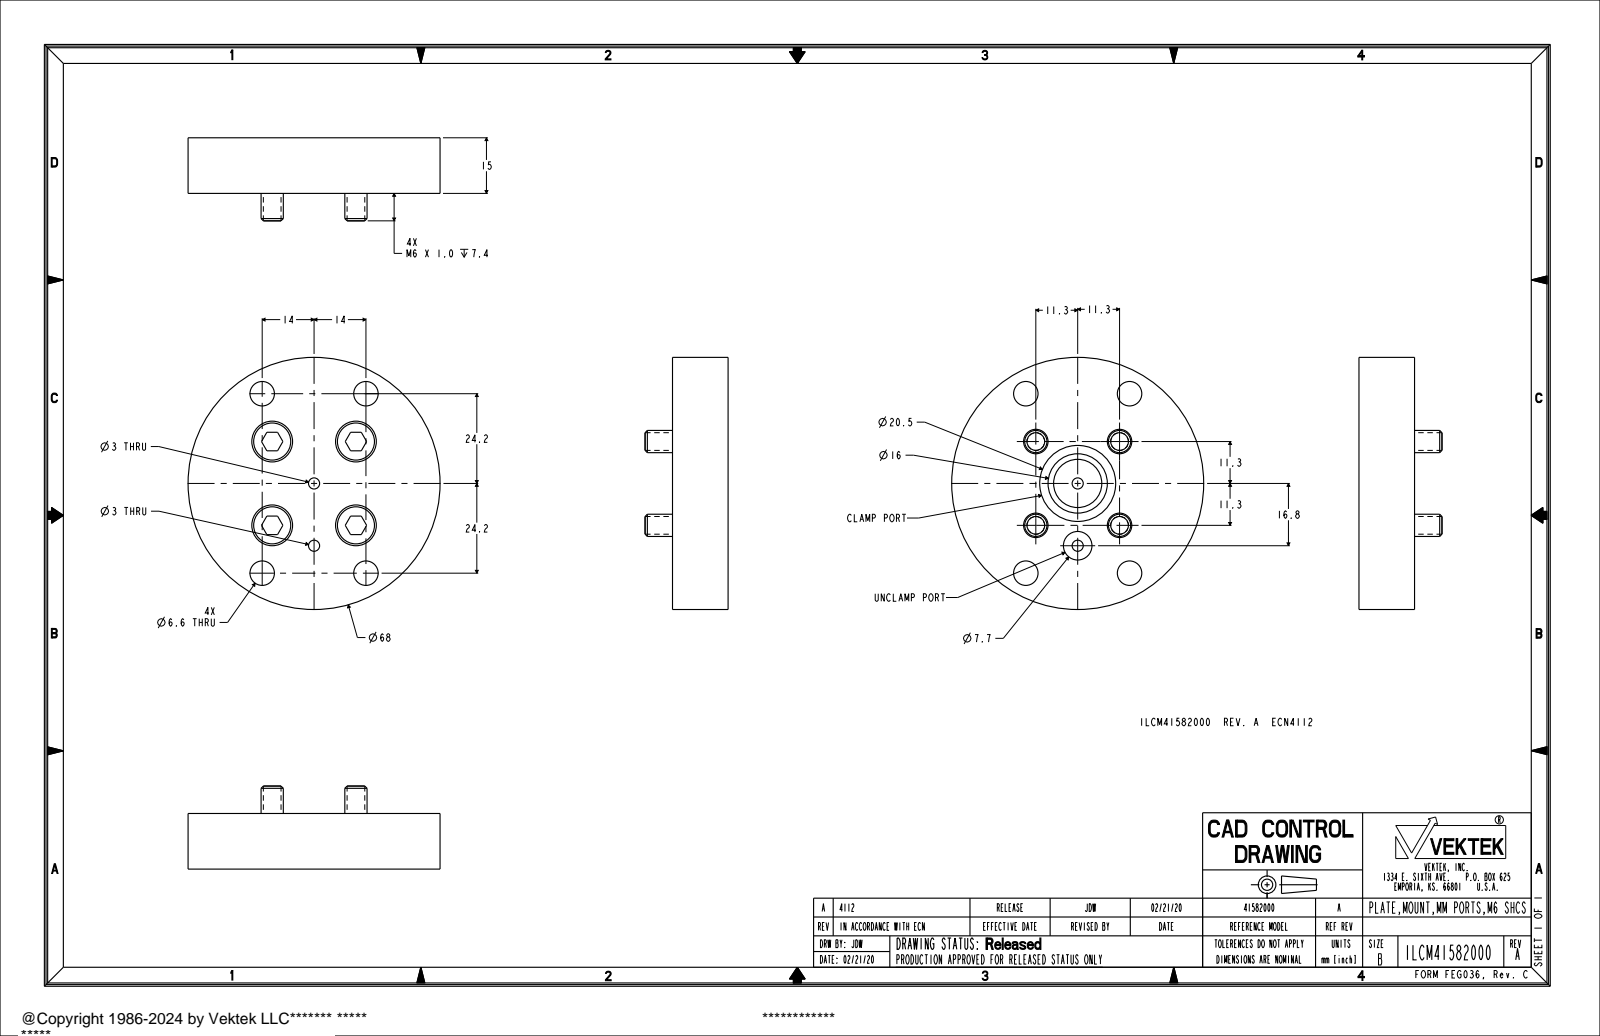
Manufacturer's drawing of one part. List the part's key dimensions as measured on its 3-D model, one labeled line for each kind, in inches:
Part name (STEP PRODUCT): ILCM41582000
STEP written by: PRO/ENGINEER BY PARAMETRIC TECHNOLOGY CORPORATION, 2013320 (AUTOMOTIVE_DESIGN)
Units: inches
Bodies: 1 solid, 127 faces (57 planar, 60 cylindrical, 10 other)
Overall size (bounding box): 2.677 × 2.677 × 0.882
Volume: 3.08 in³ · Surface area: 26 in²
Round holes (diameter × count): ⌀0.26 ×8, ⌀0.433 ×4, ⌀0.118 ×2, ⌀0.303 ×1, ⌀0.63 ×1, ⌀0.807 ×1
Round bosses / shafts (diameter × count): ⌀0.394 ×4, ⌀0.236 ×4, ⌀0.188 ×4, ⌀2.677 ×1
Main face-to-face distances: 0.591, 0.016, 0.575, 0.236, 0.339, 0.118, 0.531, 0.882, 0.866, 0.291
Hole centre spacings: 0.519, 0.629, 0.89, 1.101, 1.118, 1.402, 1.716, 0.495
